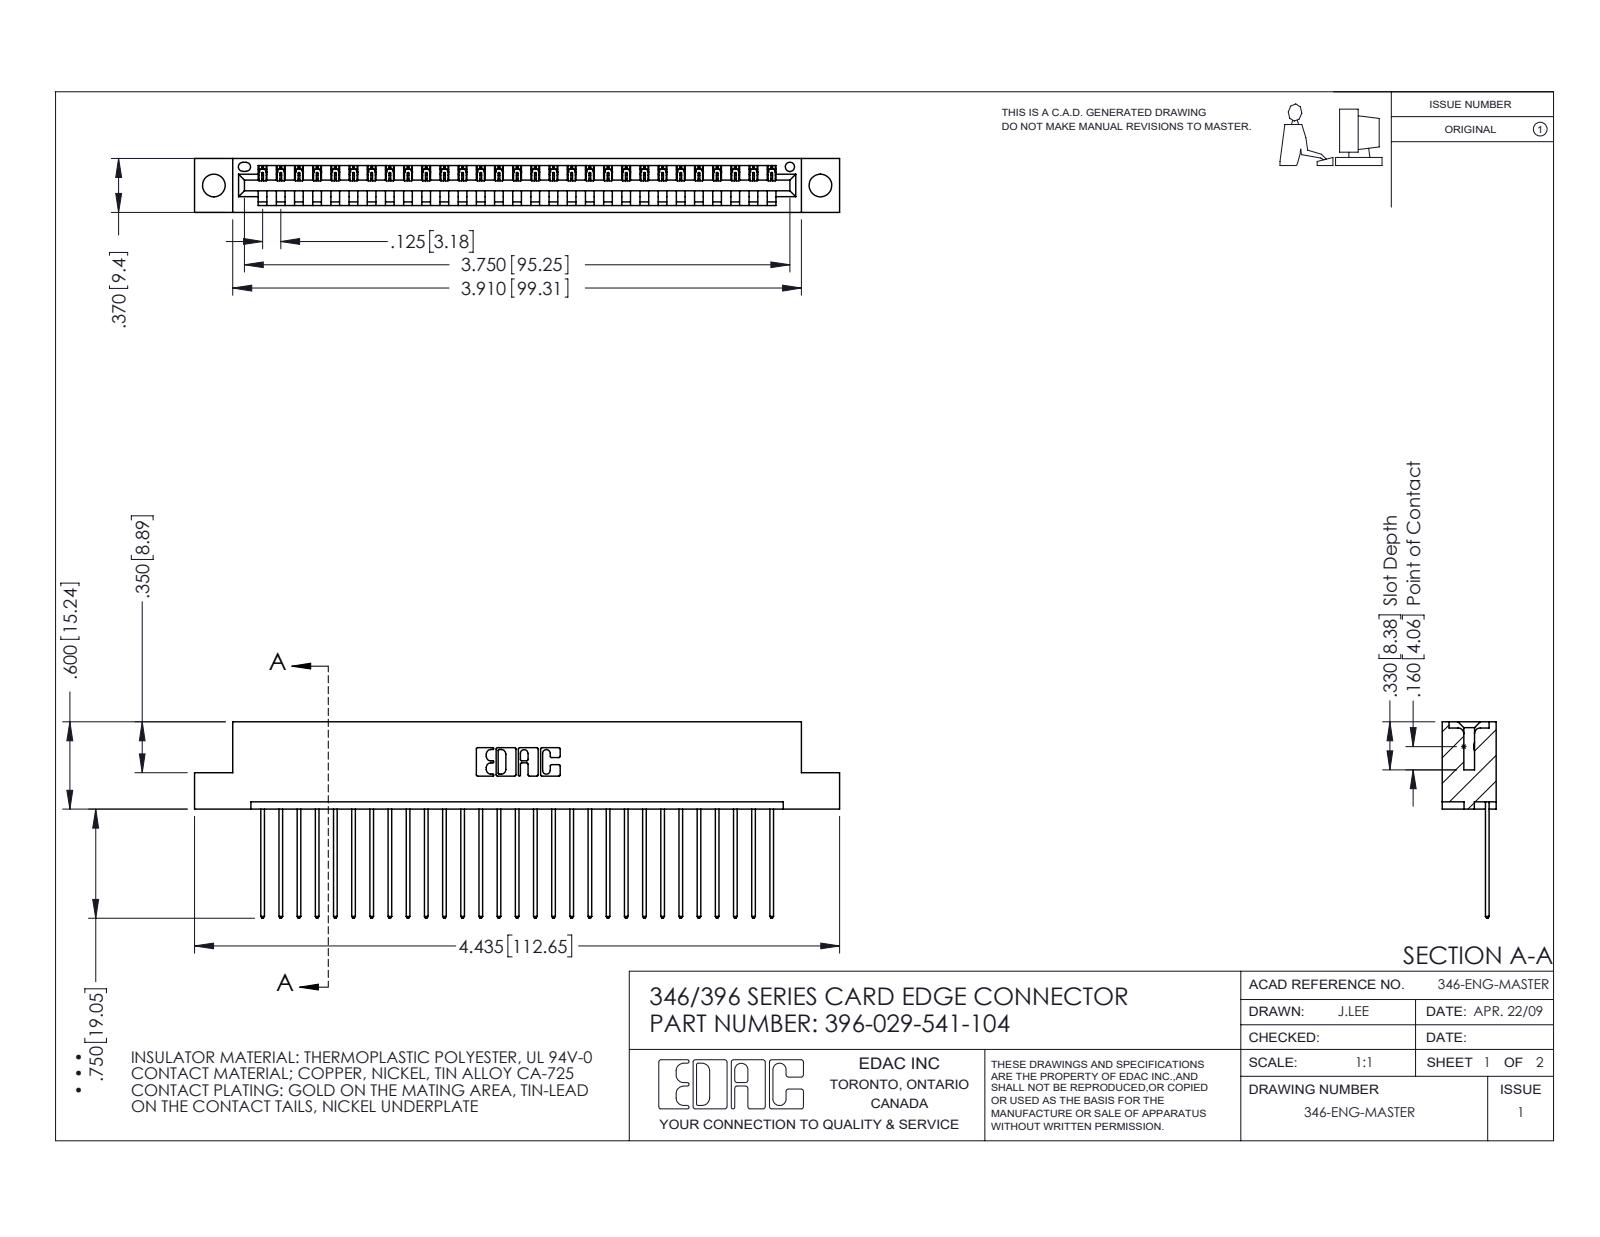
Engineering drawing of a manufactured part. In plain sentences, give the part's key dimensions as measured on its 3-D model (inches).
The part is named "345-292-001_345-293-141; 396-029-541-104; 346 Part_Flush Mounting Lugs - 0.156 Dia-TH". Its 3-D file was written by "SolidWorks 2016 (CONFIG_CONTROL_DESIGN)". It is 30 solids with 1804 faces: 1236 planar, 568 cylindrical and 0 other. Overall it measures 4.435 by 1.35 by 0.37 inches. Its volume is 0.653 cubic inches and its surface area 21.1 square inches. Round holes: 2 of diameter 0.156, 1 of diameter 0.064. Partial cylindrical surfaces (rounded edges, fillets, slot ends): 58 of radius 0.006, 58 of radius 0.01, 22 of radius 0.01, 6 of radius 0.007, 6 of radius 0.031, 3 of radius 0.026, 2 of radius 0.031, 2 of radius 0.04. The main face-to-face distances are 0.048, 0.322, 0.37, 0.25, 0.072, 0.298, 0.025, 0.148, 0.222, 0.1. The hole center spacings are 0.246, 3.962, 4.17.
